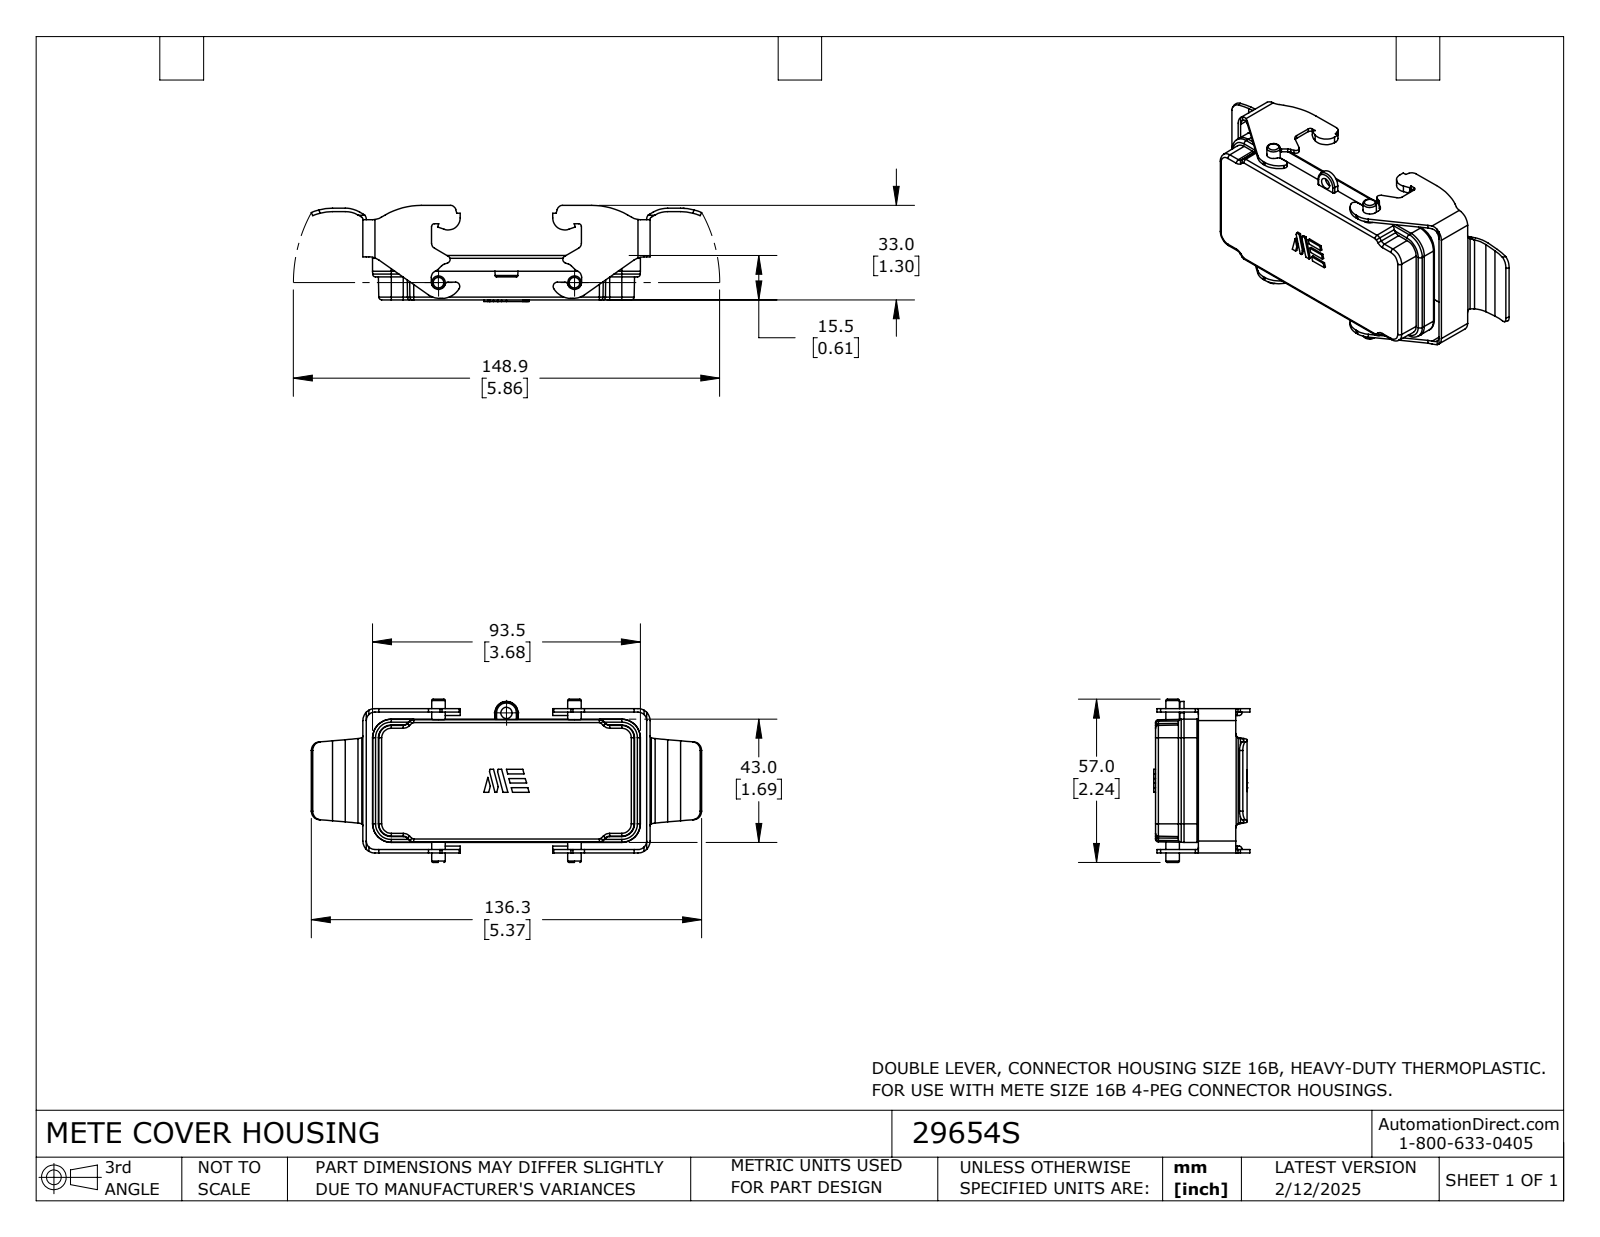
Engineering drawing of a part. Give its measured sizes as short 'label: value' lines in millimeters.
name: 29654S
written by: SolidWorks 2024 (CONFIG_CONTROL_DESIGN)
unit: mm
bodies: 1 solid, 506 faces (206 planar, 216 cylindrical, 84 other)
size: 136.3 × 57 × 33.6
volume: 23 730 mm³; area: 26 460 mm²
bosses: 2× ⌀4.7
rounds: 32× R0.2, 32× R1, 14× R0.5, 10× R3, 6× R1.5, 6× R2, 6× R2.5, 6× R4.2
face distances: 1.2, 2, 49.2, 3.7, 48, 50.4, 99.1, 43, 2.6, 6.2
